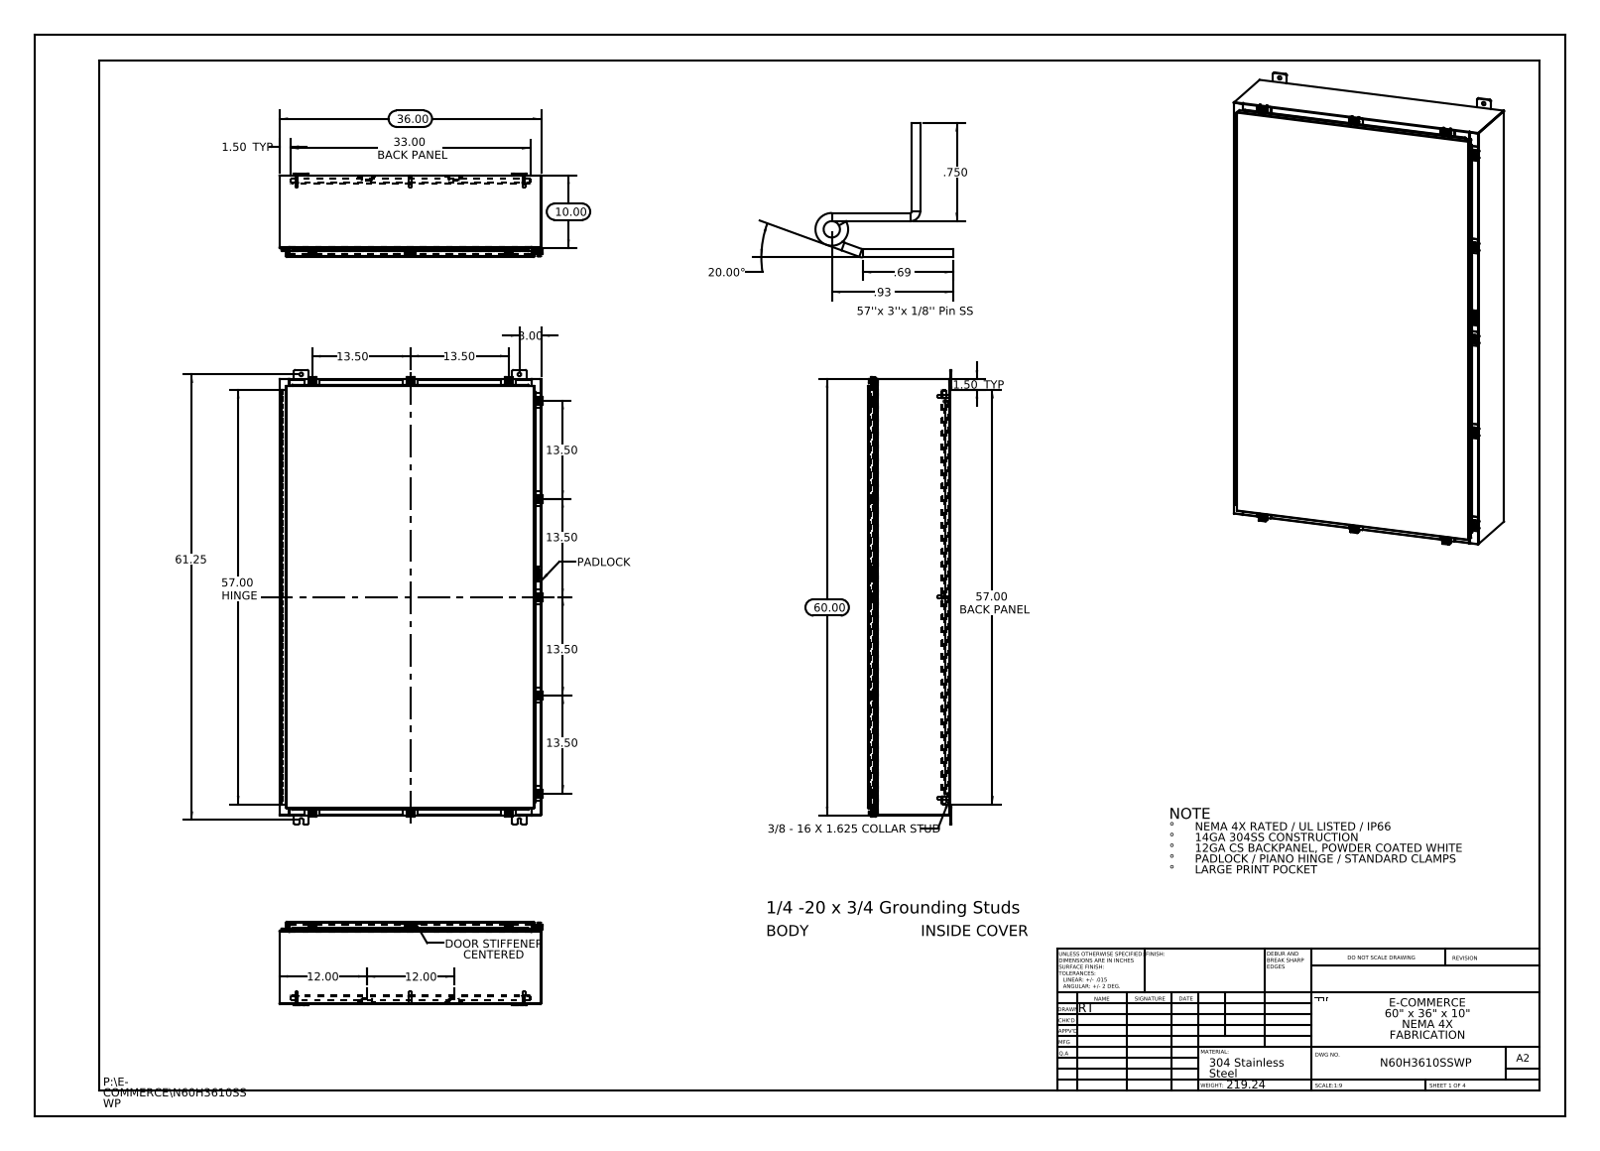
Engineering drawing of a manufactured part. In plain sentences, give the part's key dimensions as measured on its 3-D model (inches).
The part is named "N60H3610SSWP Standard Clamps; N60H3610SSWP 22101002; N60H3610SSWP Mounting Studs; N60H3610SSWP Clamp Top (+8 more)". Its 3-D file was written by "SolidWorks 2013 (CONFIG_CONTROL_DESIGN)". It is 79 solids with 3408 faces: 1766 planar, 1466 cylindrical and 176 other. Overall it measures 62.5 by 36.211 by 11.389 inches. Its volume is 767.4 cubic inches and its surface area 19 084 square inches. Round holes: 12 of diameter 0.5, 11 of diameter 0.213, 11 of diameter 0.26, 8 of diameter 0.25, 2 of diameter 0.125, 1 of diameter 0.125. Round bosses or shafts: 12 of diameter 0.25, 11 of diameter 0.5, 11 of diameter 0.399, 8 of diameter 0.625, 8 of diameter 0.375, 8 of diameter 0.33. Partial cylindrical surfaces (rounded edges, fillets, slot ends): 50 of radius 0.06, 39 of radius 0.013, 33 of radius 0.088, 24 of radius 0.19, 22 of radius 0.12, 22 of radius 0.141, 17 of radius 0.05, 16 of radius 0.08. The main face-to-face distances are 0.075, 11.126, 11.051, 0.104, 11.201, 1, 10.126, 1.075, 10.051, 1.179. The hole center spacings are 13.5, 13.663, 2.225, 27, 27.625, 29.802, 41.709, 57.39.
